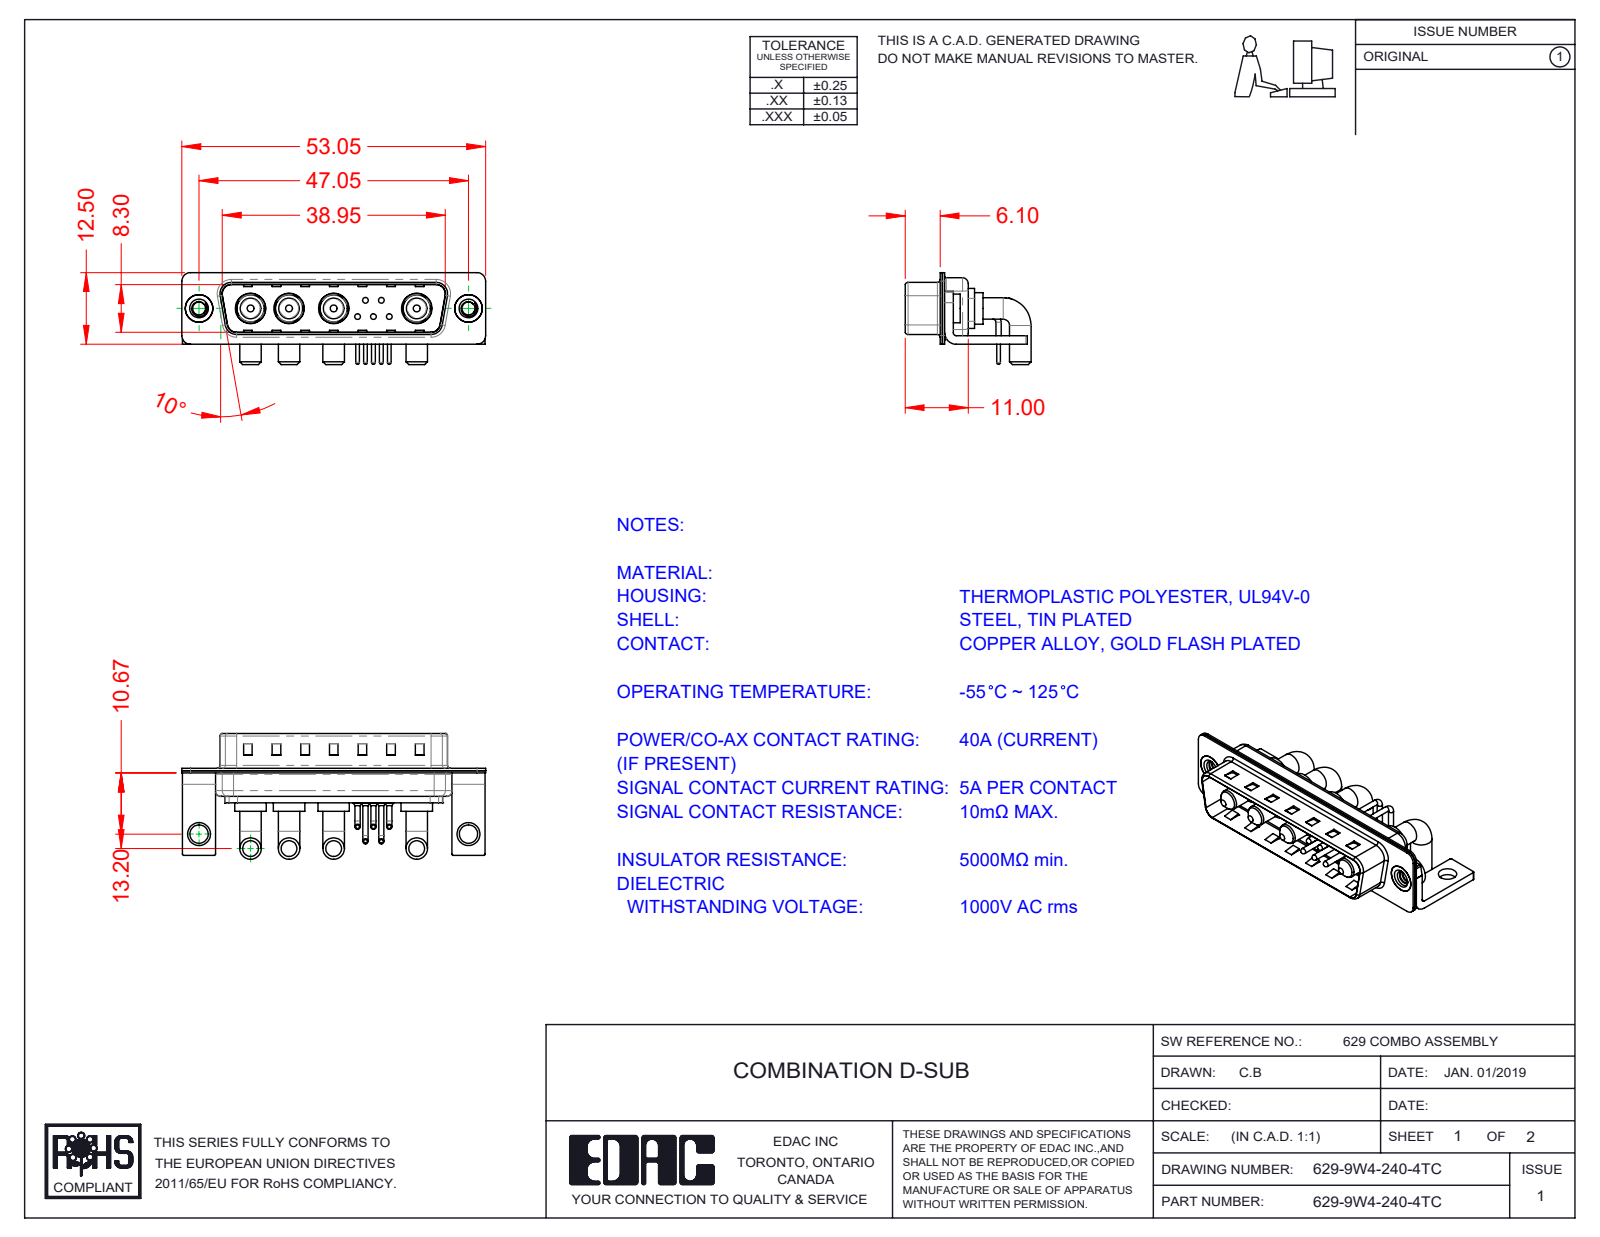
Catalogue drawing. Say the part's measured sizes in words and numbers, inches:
The part is named "629Combo Contact Row 2; 629Combo Contact Row 1; 629-9W4-240-4TC; 629Combo Stabilizer Bracket (+5 more)". Its 3-D file was written by "SolidWorks 2020 (CONFIG_CONTROL_DESIGN)". It is 20 solids with 1146 faces: 551 planar, 425 cylindrical and 170 other. Overall it measures 2.089 by 0.865 by 0.632 inches. Its volume is 0.238 cubic inches and its surface area 12.51 square inches. Round holes: 5 of diameter 0.03, 5 of diameter 0.063, 5 of diameter 0.079, 4 of diameter 0.191, 4 of diameter 0.209, 2 of diameter 0.089, 2 of diameter 0.126, 2 of diameter 0.157, 2 of diameter 0.189. Round bosses or shafts: 10 of diameter 0.035, 8 of diameter 0.148, 5 of diameter 0.059, 5 of diameter 0.039, 5 of diameter 0.026, 4 of diameter 0.217, 4 of diameter 0.205, 4 of diameter 0.187. Partial cylindrical surfaces (rounded edges, fillets, slot ends): 16 of radius 0.01, 16 of radius 0.059, 13 of radius 0.079, 9 of radius 0.02, 8 of radius 0.063, 5 of radius 0.04, 4 of radius 0.024, 4 of radius 0.026. The main face-to-face distances are 0.016, 0.031, 0.374, 0.358, 0.343, 0.059, 0.39, 0.047, 0.205, 0.024. The hole center spacings are 0.124, 0.109, 0.198, 0.571, 1.852, 0.109, 0.173, 0.174.
